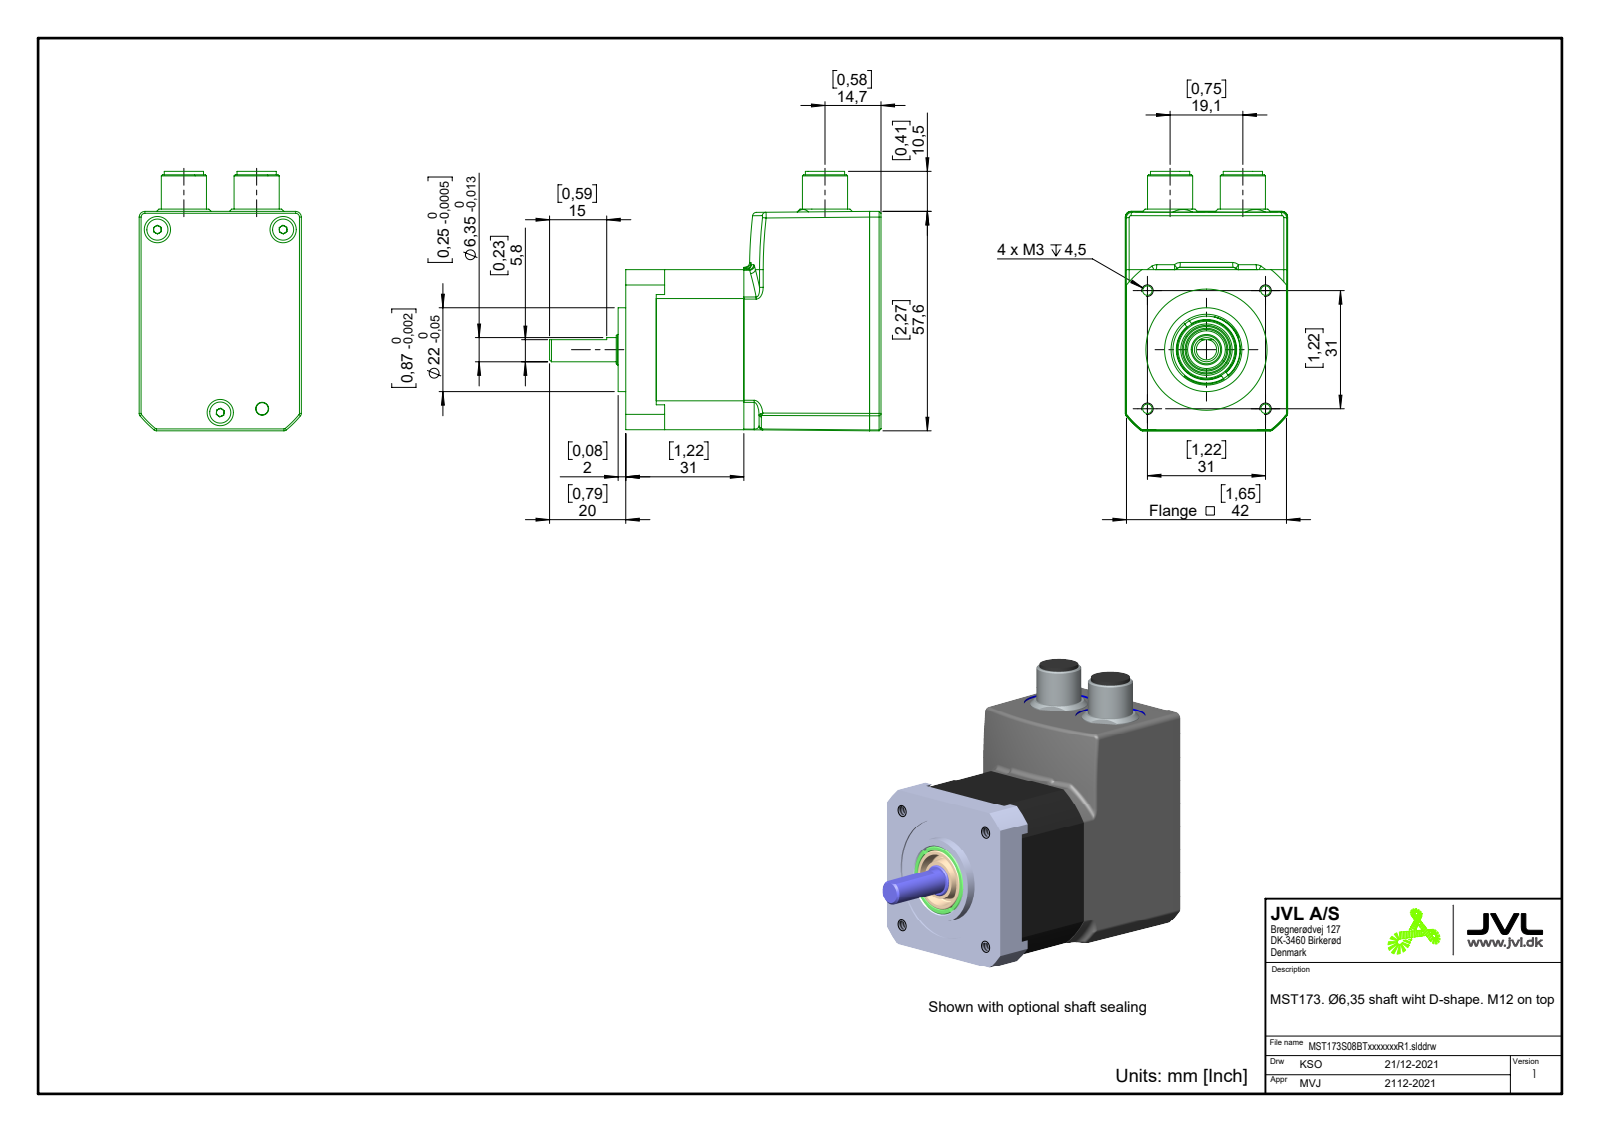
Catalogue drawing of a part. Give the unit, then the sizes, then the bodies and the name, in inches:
Units: inches
Overall size (bounding box): 3.425 × 2.68 × 1.676
Round holes (diameter × count): ⌀0.098 ×4, ⌀0.13 ×3, ⌀0.724 ×2, ⌀0.11 ×1, ⌀0.134 ×1, ⌀0.354 ×1, ⌀1.252 ×1
Round bosses / shafts (diameter × count): ⌀0.218 ×3, ⌀0.118 ×3, ⌀0.594 ×2, ⌀0.467 ×2, ⌀0.406 ×2, ⌀0.866 ×1, ⌀0.61 ×1, ⌀0.547 ×1
Partial cylindrical surfaces — rounded edges, fillets, slot ends (radius × count): R0.039 ×13, R0.059 ×2, R0.346 ×1, R0.981 ×1, R1.004 ×1, R1.063 ×1, R1.074 ×1, R3.15 ×1
Main face-to-face distances: 1.654, 2.638, 0.079, 2.618, 0.02, 1.665, 0.059, 2.559, 0.098, 0.157
Hole centre spacings: 0.863, 1.22, 1.4, 0.611, 0.631, 1.409, 1.726, 1.851
Volume: 8.548 in³ · Surface area: 30.64 in²
Bodies: 5 solids, 328 faces (134 planar, 71 cylindrical, 123 other)
Part name (STEP PRODUCT): MST173S08BTxxxxxxx
STEP written by: SolidWorks 2020 (AUTOMOTIVE_DESIGN)
